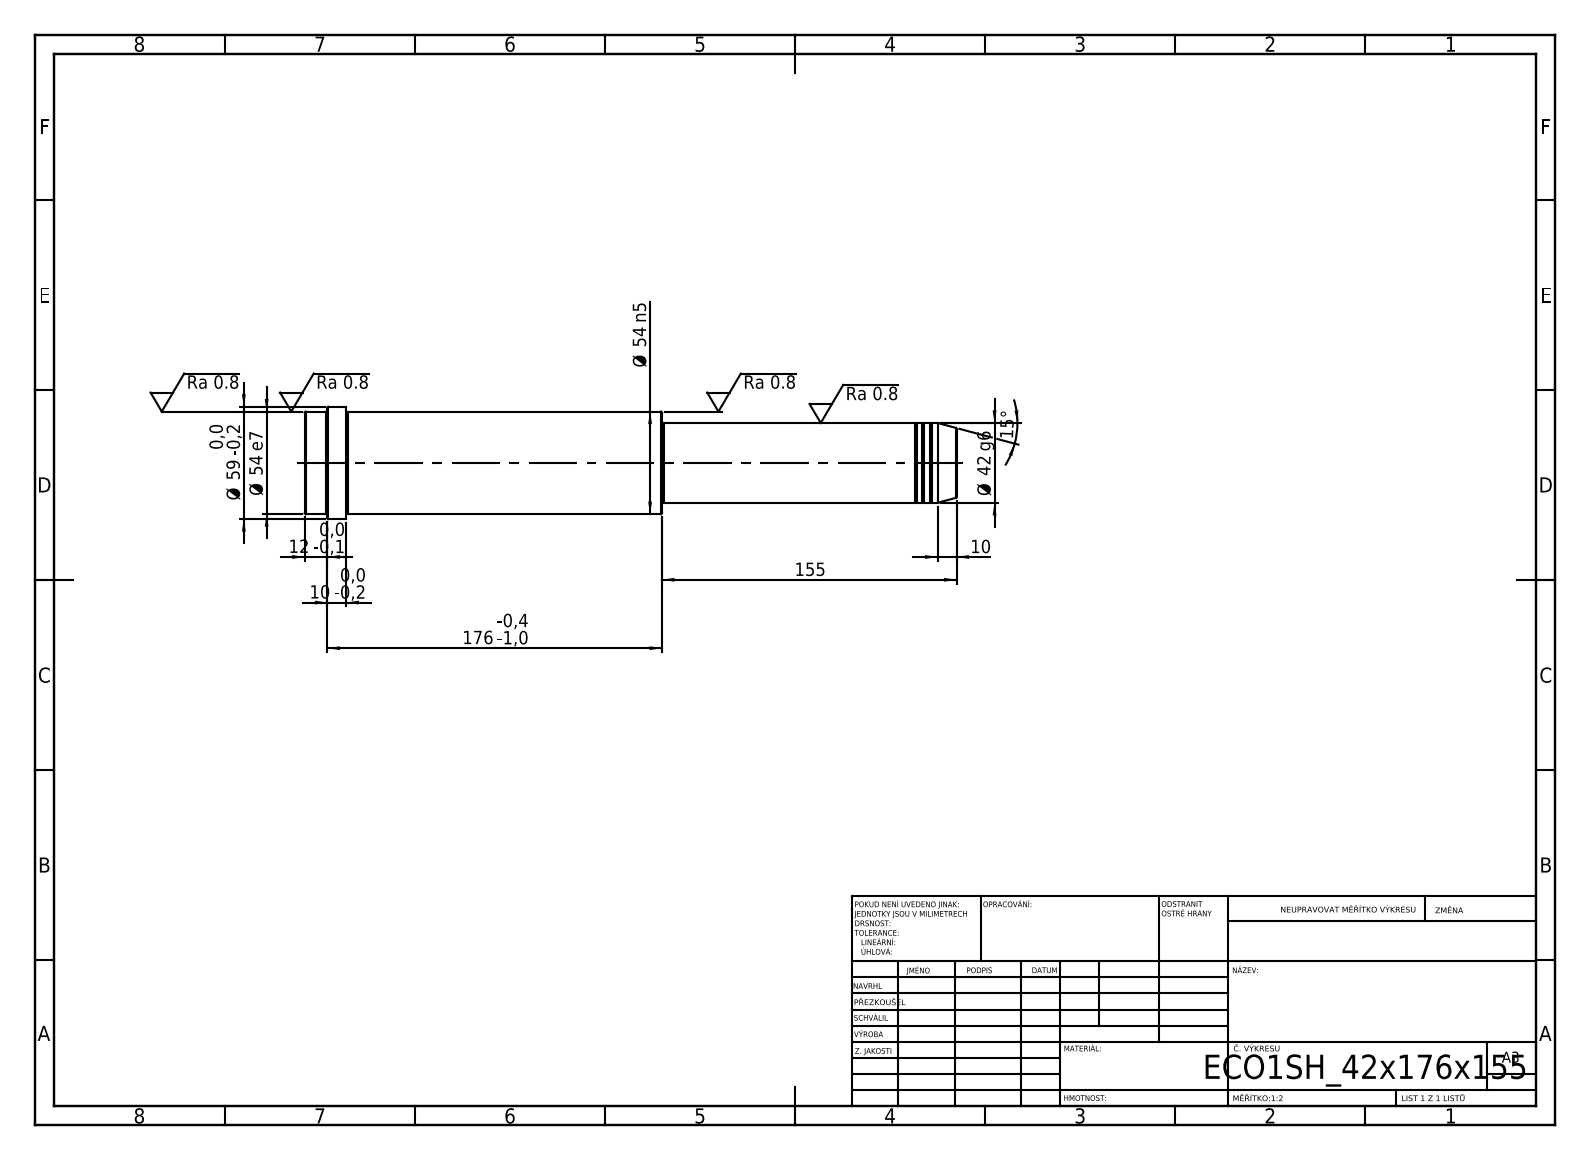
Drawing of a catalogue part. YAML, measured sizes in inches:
step_written_by: "SolidWorks 2019 (CONFIG_CONTROL_DESIGN)"
units: inches
bodies: {solids: 1, faces: 52, planar: 6, cylindrical: 16, other: 30}
overall_size: [13.504, 2.323, 2.323]
volume: 39.52
surface_area: 89.84
round_bosses_or_shafts:
  - {diameter: 2.323, count: 1}
  - {diameter: 2.126, count: 1}
  - {diameter: 1.654, count: 1}
  - {diameter: 1.614, count: 1}
face_to_face_distances: [13.504, 6.102, 7.402, 12.638, 6.535, 0.866, 13.031, 6.929, 0.394, 0.472]
